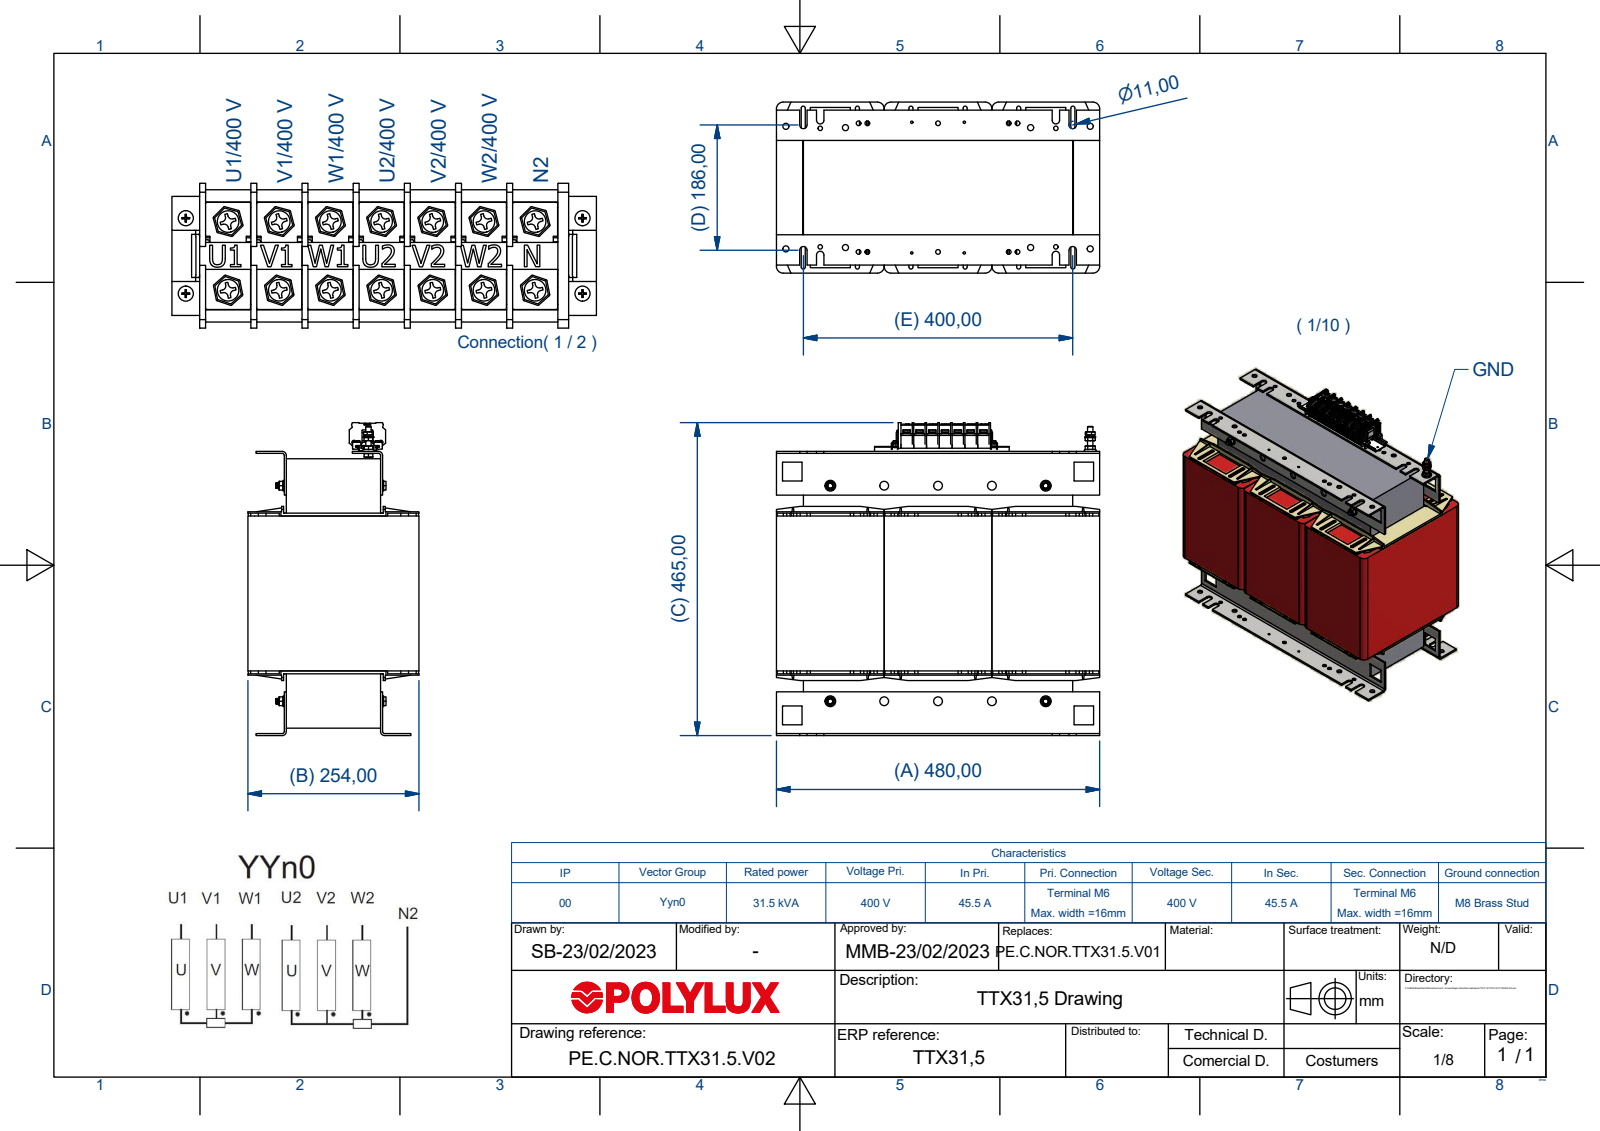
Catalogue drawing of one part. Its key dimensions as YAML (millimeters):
part_name: "TTX31.5"
step_written_by: "Autodesk Inventor 2018 (AUTOMOTIVE_DESIGN)"
units: millimeters
bodies: {solids: 106, faces: 7971, planar: 2923, cylindrical: 2991, other: 2057}
overall_size: [480, 463.11, 254]
volume: 38090000
surface_area: 3293000
round_holes:
  - {diameter: 9, count: 16}
  - {diameter: 7, count: 15}
  - {diameter: 5, count: 14}
  - {diameter: 5.3, count: 14}
  - {diameter: 5.4, count: 14}
  - {diameter: 8, count: 14}
  - {diameter: 6.65, count: 11}
  - {diameter: 13, count: 10}
  - {diameter: 3.5, count: 6}
  - {diameter: 4.2, count: 2}
  - {diameter: 4.45, count: 2}
  - {diameter: 4.25, count: 1}
round_bosses_or_shafts:
  - {diameter: 10, count: 14}
  - {diameter: 9.2, count: 14}
  - {diameter: 7.7, count: 14}
  - {diameter: 5.85, count: 14}
  - {diameter: 16, count: 5}
  - {diameter: 8, count: 5}
  - {diameter: 3.92, count: 4}
  - {diameter: 3, count: 4}
partial_cylinders:
  - {radius: 0.15, count: 1208}
  - {radius: 0.5, count: 132}
  - {radius: 0.1, count: 80}
  - {radius: 1.5, count: 56}
  - {radius: 3, count: 28}
  - {radius: 1, count: 20}
  - {radius: 0.55, count: 14}
  - {radius: 5.5, count: 12}
face_to_face_distances: [160, 320, 34.5, 125.5, 146, 3, 1, 91, 6, 285.5]
hole_center_spacings: [80, 329.85, 320, 105, 160, 357.77, 13, 118]
